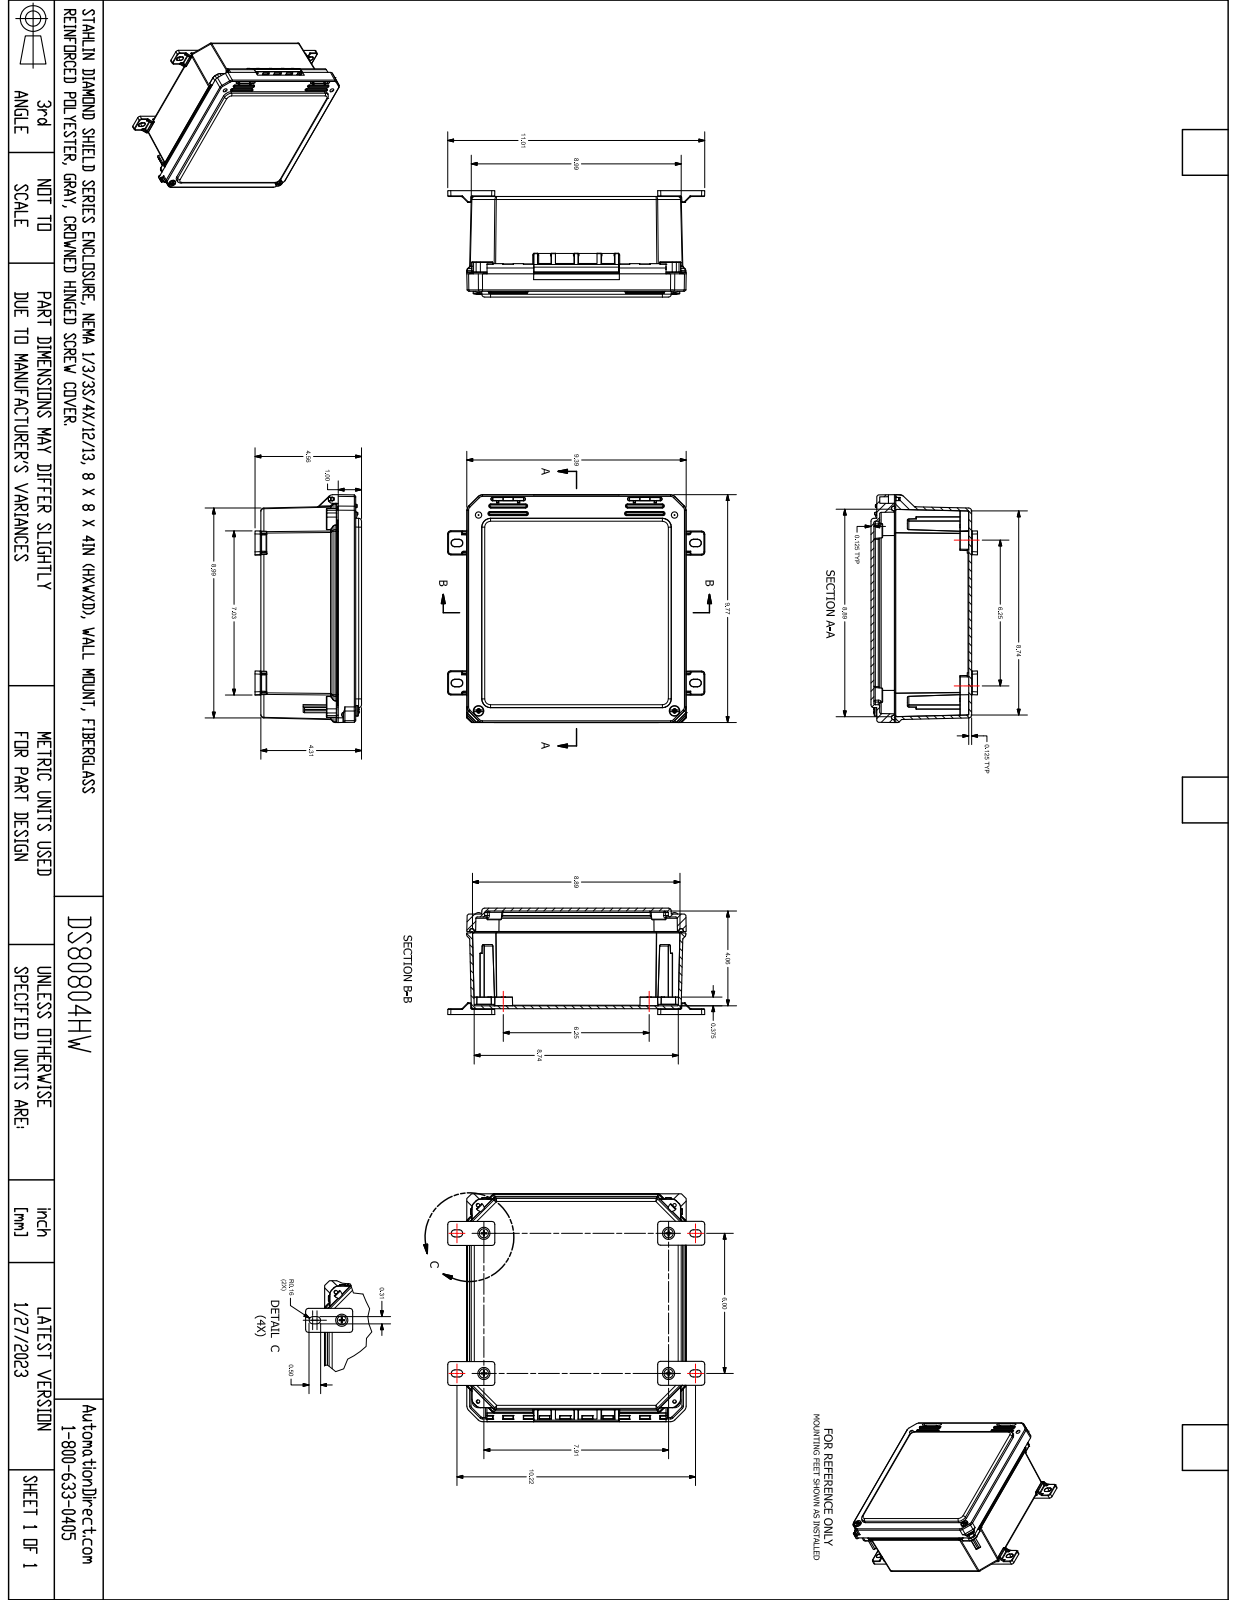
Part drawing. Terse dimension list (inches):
name: FR80804HW
written by: SolidWorks 2021 (AUTOMOTIVE_DESIGN)
unit: in
bodies: 23 solids, 2085 faces (633 planar, 819 cylindrical, 633 other)
size: 9.78 × 9.404 × 4.597
volume: 51.49 in³; area: 710.4 in²
holes: 8× ⌀0.152, 8× ⌀0.159, 4× ⌀0.137, 4× ⌀0.156, 4× ⌀0.252, 4× ⌀0.253, 2× ⌀0.15, 2× ⌀0.219, 2× ⌀0.227, 2× ⌀0.313
bosses: 8× ⌀0.27, 4× ⌀0.87, 4× ⌀0.262, 2× ⌀0.45, 2× ⌀0.209, 2× ⌀0.199, 2× ⌀0.135, 1× ⌀0.435
rounds: 117× R0.01, 94× R0.005, 77× R0.02, 50× R0.03, 28× R0.063, 24× R0.03, 24× R0.09, 23× R0.096
face distances: 0.125, 0.125, 4.059, 4.184, 4.309, 4.184, 3.934, 0.25, 0.375, 0.124
hole spacings: 7.41, 8.392, 7.75, 8.392, 0.837, 6.25, 7.079, 7.411
